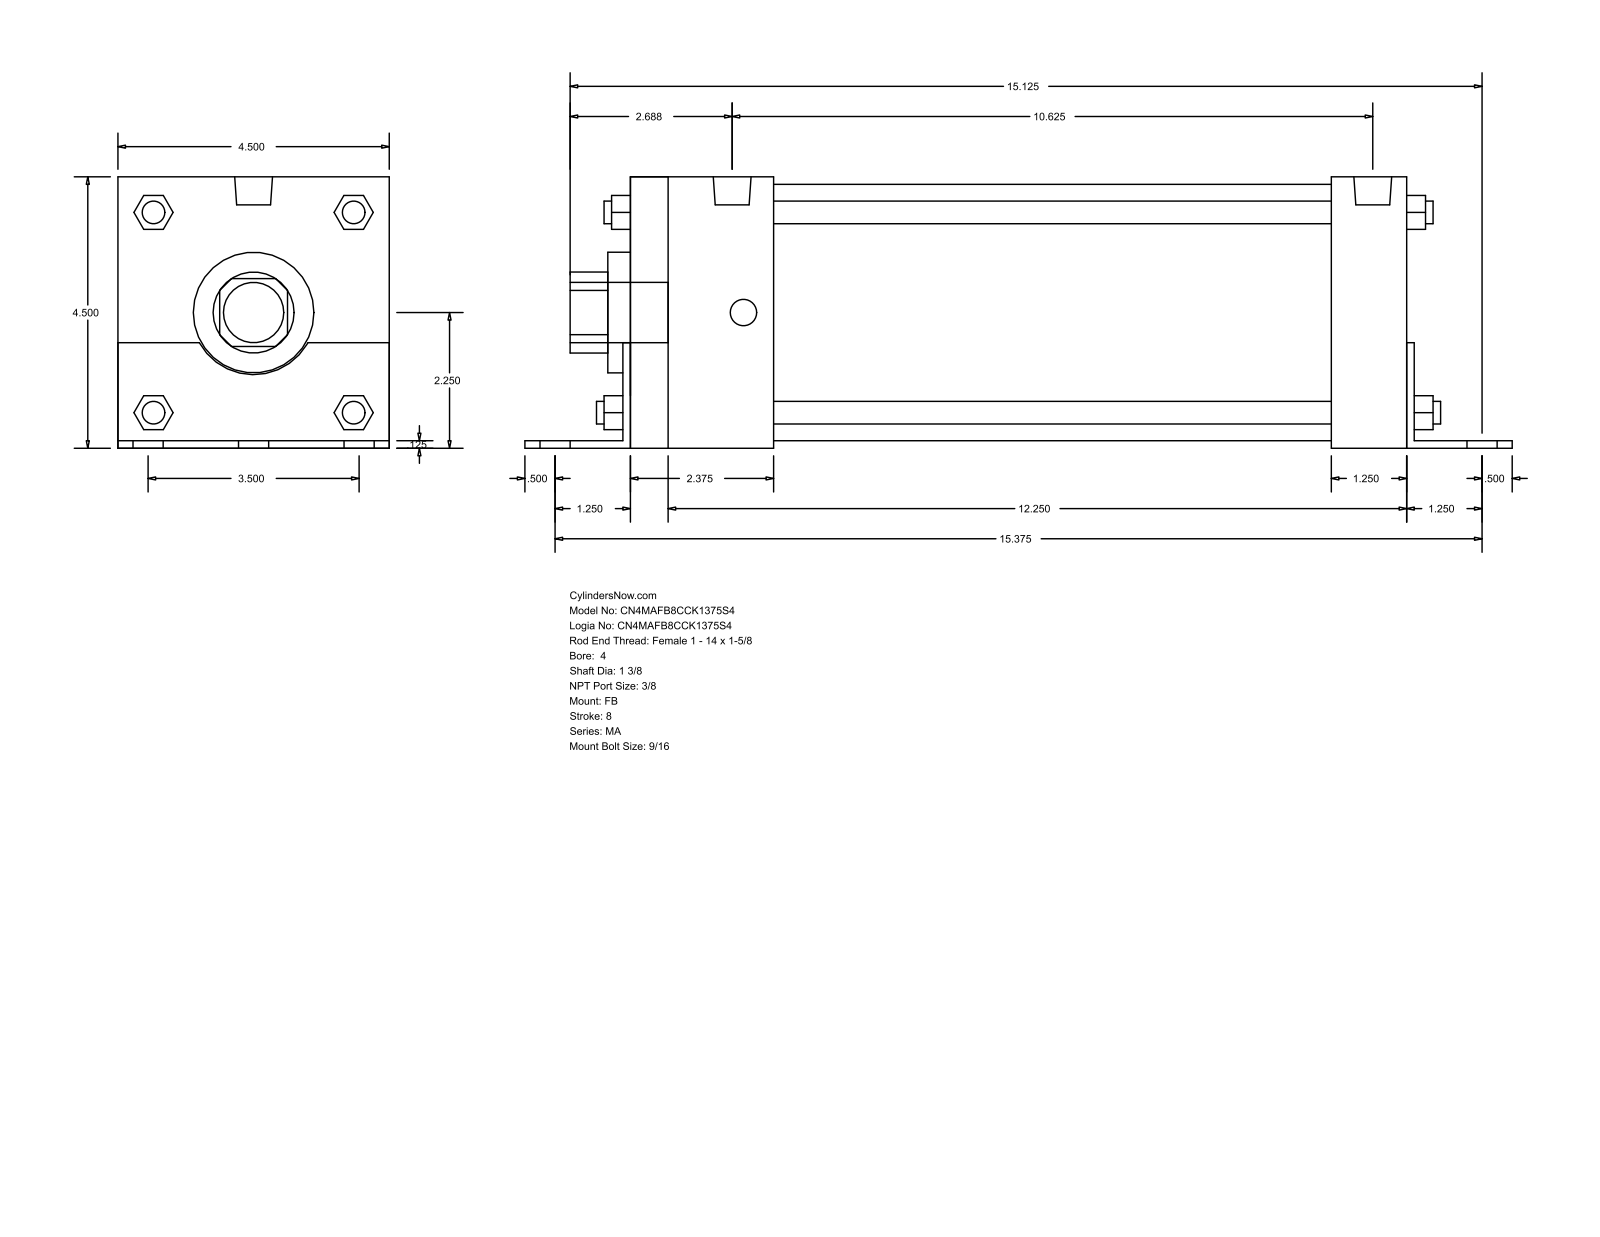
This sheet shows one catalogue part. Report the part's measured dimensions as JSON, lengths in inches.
{"part_name": "MA_FB__0400_1.375", "step_written_by": "GSSL Pune (CONFIG_CONTROL_DESIGN)", "units": "inches", "bodies": {"solids": 0, "faces": 140, "planar": 105, "cylindrical": 35, "other": 0}, "overall_size": [16.375, 4.502, 4.5], "round_holes": [[1.375, 1], [2, 1], [4.25, 1]], "round_bosses_or_shafts": [[0.563, 6], [0.437, 4], [0.375, 4], [0.627, 2], [1, 1]], "partial_cylinders_radius": [[0.672, 1], [1.03, 1]], "face_to_face_distances": [4.5, 0.125, 4.502, 0.123, 4.377, 13, 12.875, 2.375, 13.125, 1.25]}
